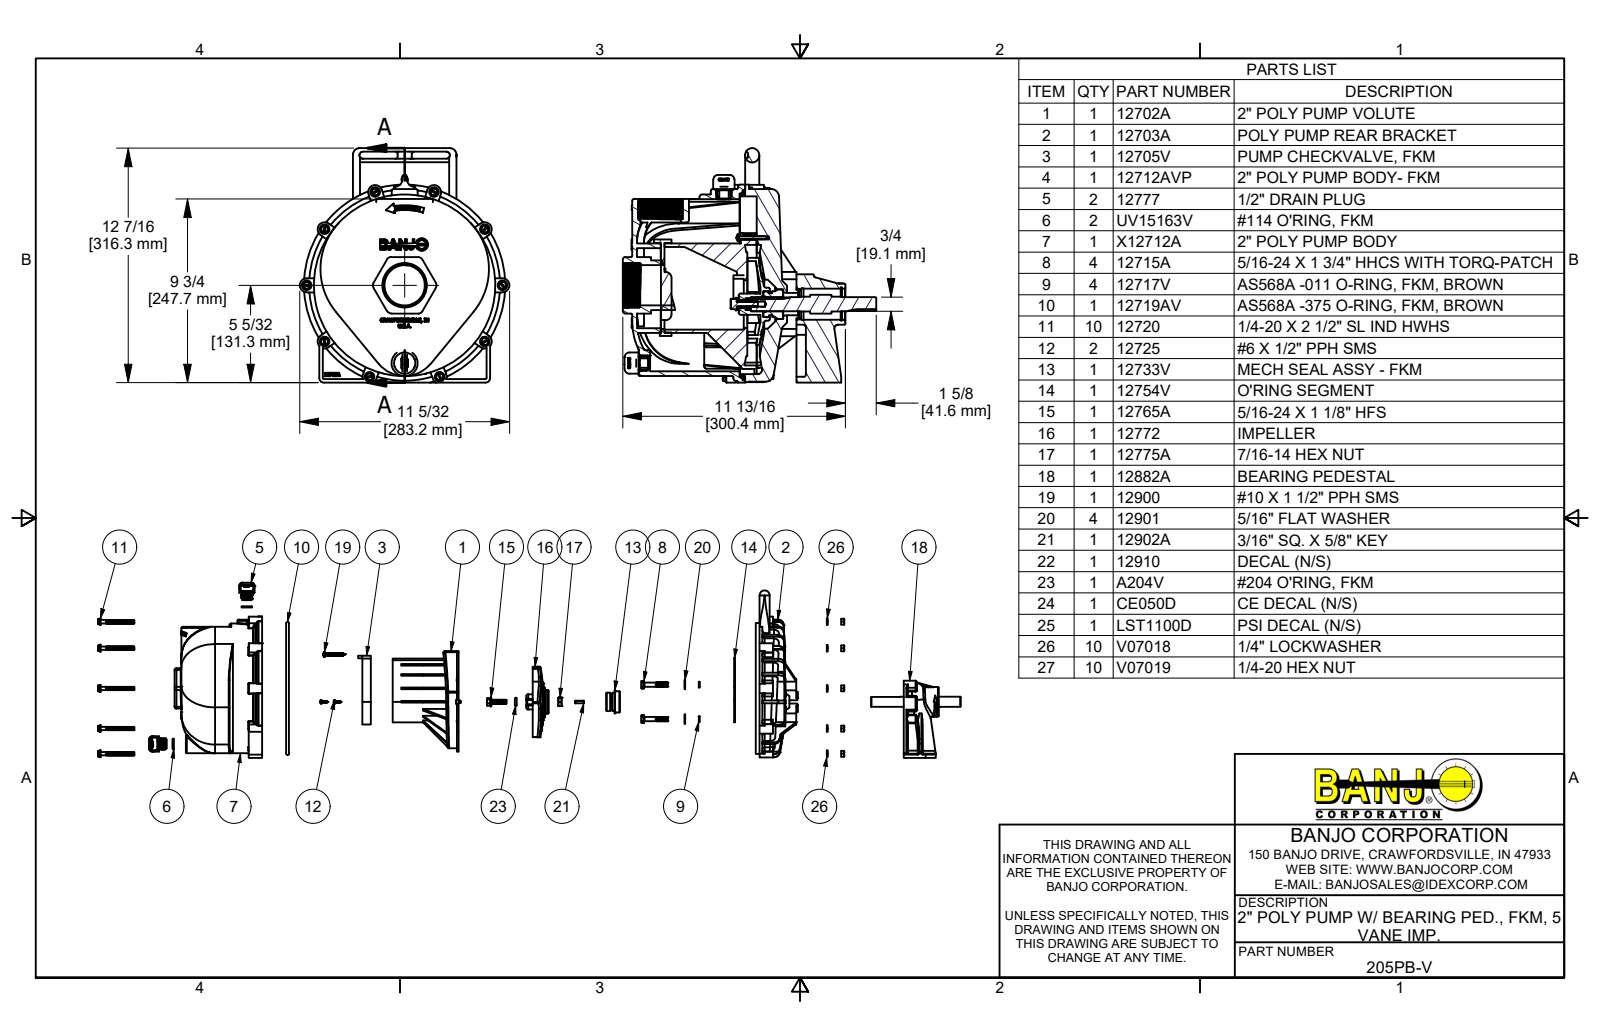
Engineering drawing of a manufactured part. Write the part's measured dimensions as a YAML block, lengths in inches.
part_name: "205PB-V; 12703A; 12712AVP; X12712A (+8 more)"
step_written_by: "Autodesk Inventor 2019 (AUTOMOTIVE_DESIGN)"
units: inches
bodies: {solids: 86, faces: 8089, planar: 2199, cylindrical: 2228, other: 3662}
overall_size: [13.823, 13.461, 11.15]
volume: 194.1
surface_area: 1899
round_holes:
  - {diameter: 0.196, count: 10}
  - {diameter: 0.252, count: 10}
  - {diameter: 0.27, count: 10}
  - {diameter: 0.22, count: 7}
  - {diameter: 0.267, count: 5}
  - {diameter: 0.344, count: 4}
  - {diameter: 0.406, count: 4}
  - {diameter: 0.469, count: 4}
  - {diameter: 0.815, count: 4}
  - {diameter: 0.078, count: 2}
  - {diameter: 0.113, count: 2}
  - {diameter: 0.115, count: 2}
round_bosses_or_shafts:
  - {diameter: 0.276, count: 80}
  - {diameter: 0.52, count: 10}
  - {diameter: 0.489, count: 10}
  - {diameter: 0.25, count: 10}
  - {diameter: 0.192, count: 6}
  - {diameter: 0.688, count: 4}
  - {diameter: 0.313, count: 4}
  - {diameter: 1.13, count: 3}
partial_cylinders:
  - {radius: 0.03, count: 116}
  - {radius: 0.06, count: 77}
  - {radius: 0.25, count: 35}
  - {radius: 0.125, count: 31}
  - {radius: 0.008, count: 26}
  - {radius: 0.187, count: 24}
  - {radius: 0.015, count: 13}
  - {radius: 0.5, count: 13}
face_to_face_distances: [0.18, 0.2, 1, 0.037, 0.163, 0.25, 2.88, 0.11, 0.125, 0.5]
hole_center_spacings: [5.2, 1.81, 2.56, 3.128, 6.15, 8.387, 10.4, 1.31]
